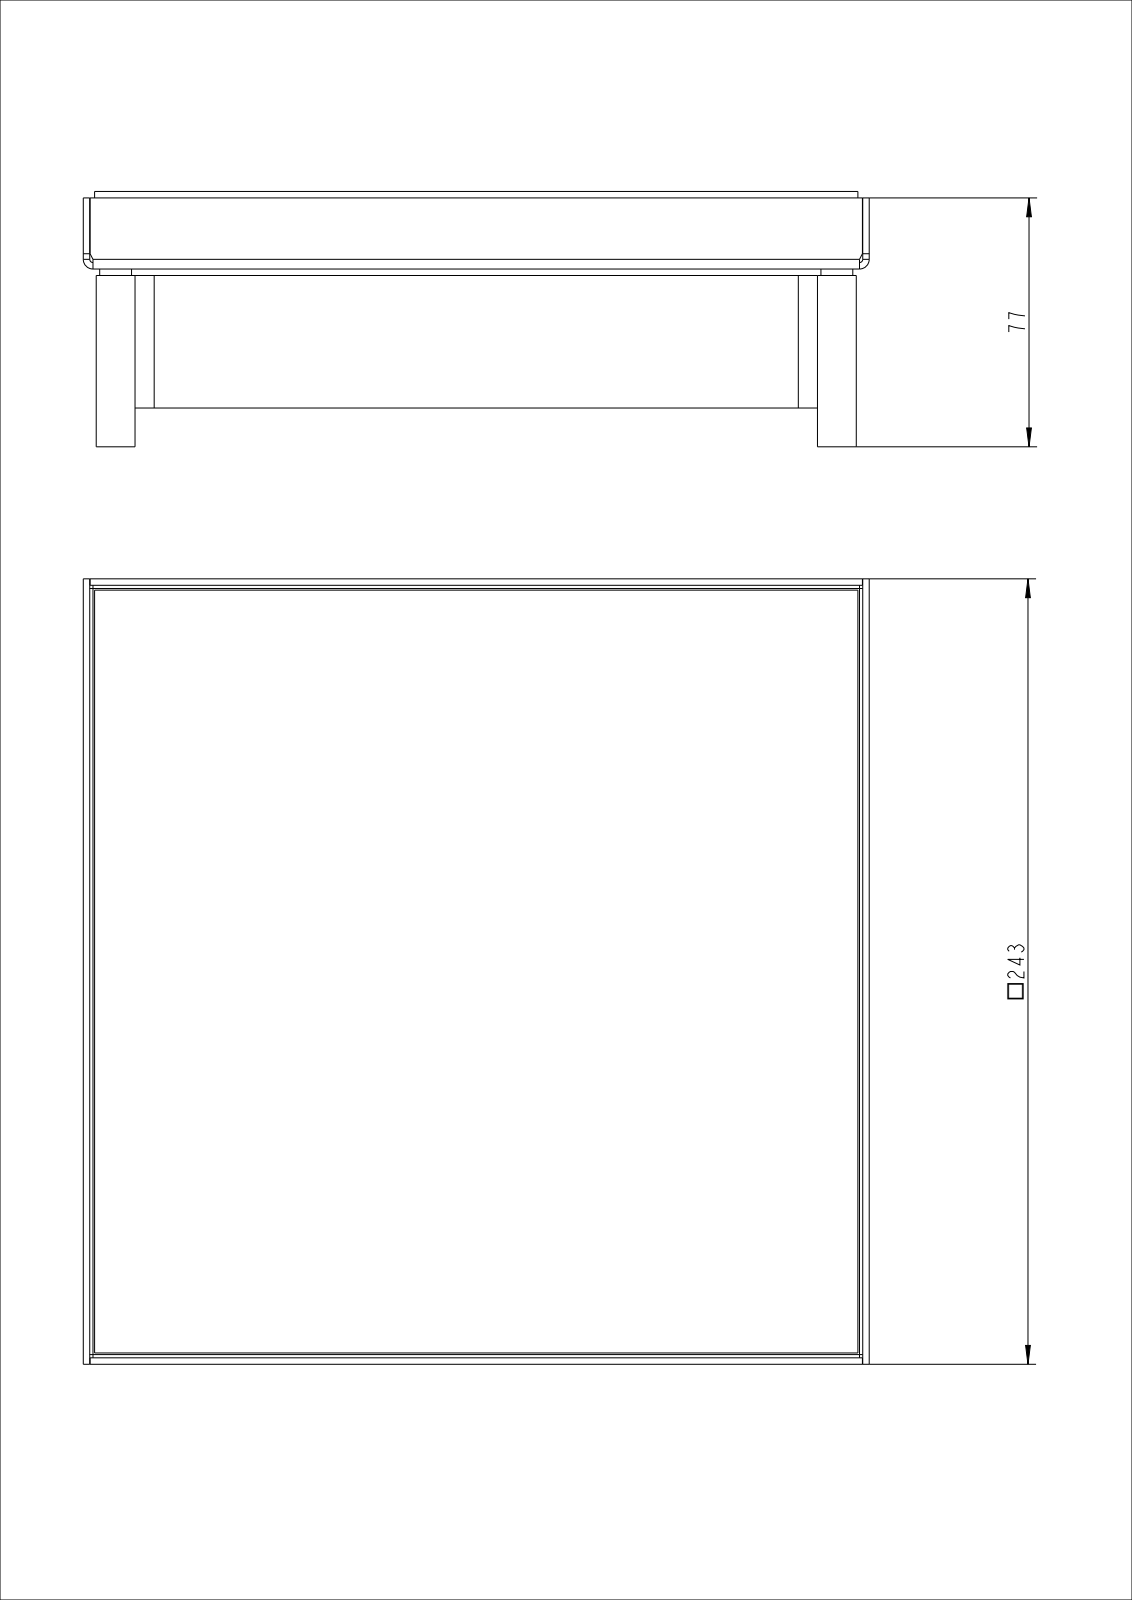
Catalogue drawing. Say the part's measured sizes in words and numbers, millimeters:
The part is named "T-00626_1; T-00632_1; T-00625_1; T-00951_1 (+2 more)". Its 3-D file was written by "CREO PARAMETRIC BY PTC INC, 2022281 (AUTOMOTIVE_DESIGN)". It is 7 solids with 126 faces: 78 planar, 48 cylindrical and 0 other. Overall it measures 243 by 243 by 79 millimeters. Its volume is 1 382 000 cubic millimeters and its surface area 281 517 square millimeters. Round holes: 4 of diameter 6.8, 4 of diameter 8.5. Round bosses or shafts: 4 of diameter 12, 4 of diameter 9.85. Partial cylindrical surfaces (rounded edges, fillets, slot ends): 4 of radius 1, 4 of radius 3, 1 of radius 150, 1 of radius 152.5. The main face-to-face distances are 22, 2.5, 2, 3.5, 237.5, 231, 6, 239.5, 241, 1.5. The hole center spacings are 223, 315.37.
